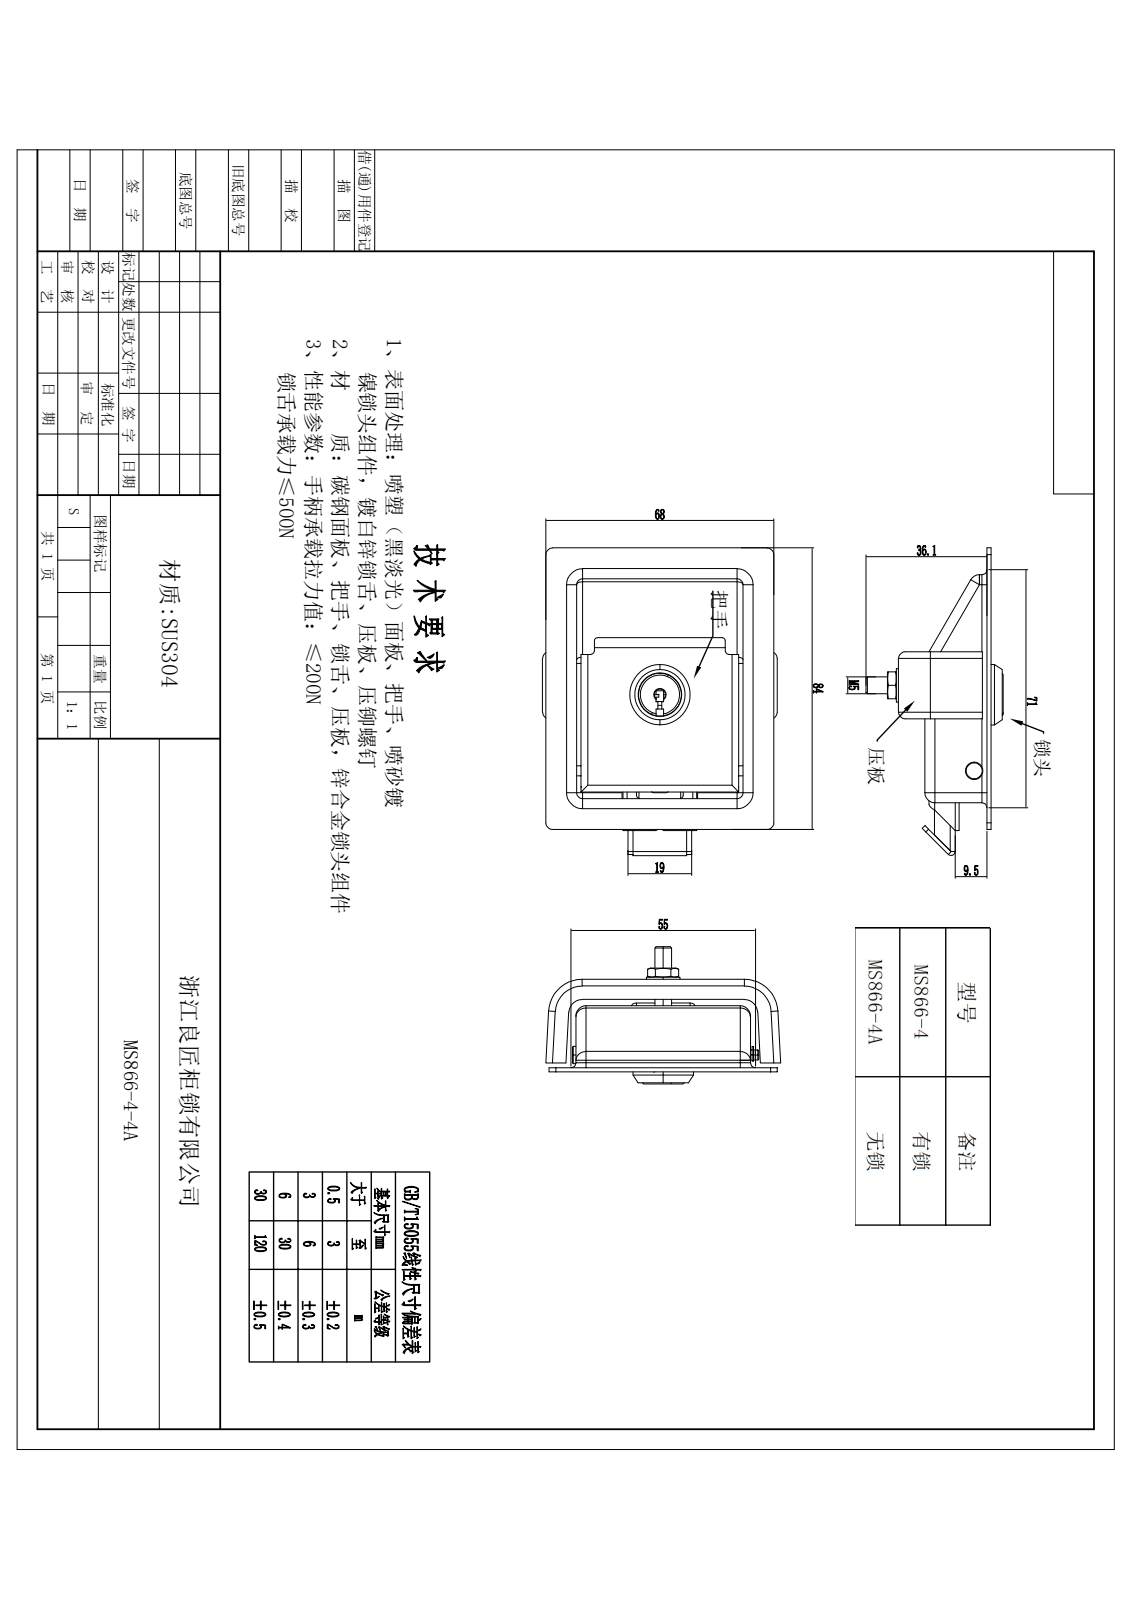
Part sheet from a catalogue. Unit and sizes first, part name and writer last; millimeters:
Units: millimetres
Overall size (bounding box): 91.8 × 70 × 40.9
Round holes (diameter × count): ⌀4.2 ×2, ⌀3.1 ×1, ⌀3.2 ×1, ⌀5 ×1, ⌀5.1 ×1, ⌀5.3 ×1, ⌀9.1 ×1, ⌀13 ×1
Round bosses / shafts (diameter × count): ⌀18 ×1, ⌀14 ×1, ⌀12.8 ×1, ⌀10 ×1, ⌀9 ×1, ⌀8 ×1, ⌀6.5 ×1, ⌀5.2 ×1
Partial cylindrical surfaces — rounded edges, fillets, slot ends (radius × count): R1 ×26, R0.5 ×22, R2 ×17, R3 ×14, R1.5 ×10, R1.8 ×10, R0.3 ×7, R0.2 ×5
Main face-to-face distances: 1.2, 18.5, 17.3, 1.5, 2.5, 48.3, 7.8, 19.7, 10.7, 50.8
Hole centre spacings: 2.8
Volume: 24 269 mm³ · Surface area: 43 853 mm²
Bodies: 25 solids, 957 faces (464 planar, 270 cylindrical, 223 other)
STEP written by: Rhino 8.5 (CONFIG_CONTROL_DESIGN)
